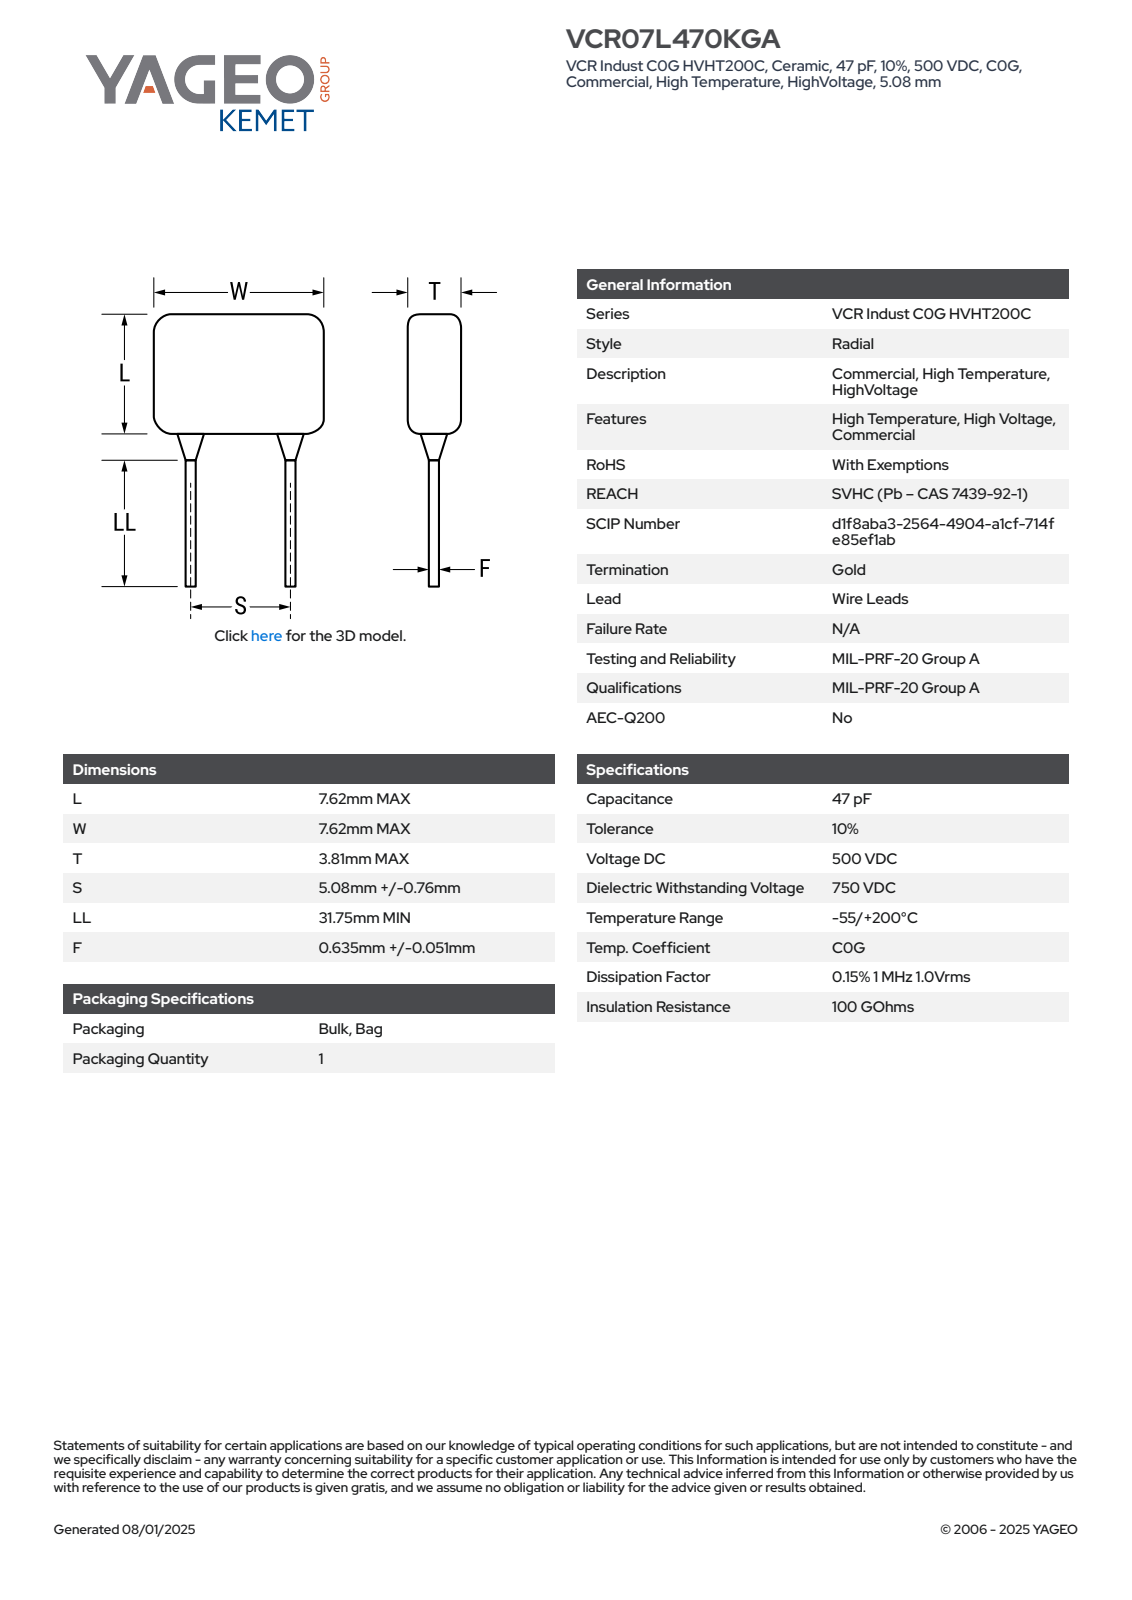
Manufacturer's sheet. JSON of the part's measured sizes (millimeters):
{"part_name": "CCRM_RMST_07_L7.62H7.62T3.81S5.08LL31.75F0.686", "step_written_by": "SolidWorks 2014 (AUTOMOTIVE_DESIGN)", "units": "millimeters", "bodies": {"solids": 4, "faces": 69, "planar": 65, "cylindrical": 4, "other": 0}, "overall_size": [39.37, 7.62, 3.81], "volume_mm3": 245, "surface_area_mm2": 380, "round_bosses_or_shafts": [[0.69, 2]], "face_to_face_distances": [3.81, 7.62, 31.75, 39.37, 36.29, 4.54, 3.08, 34.92, 3.17, 1.37]}
